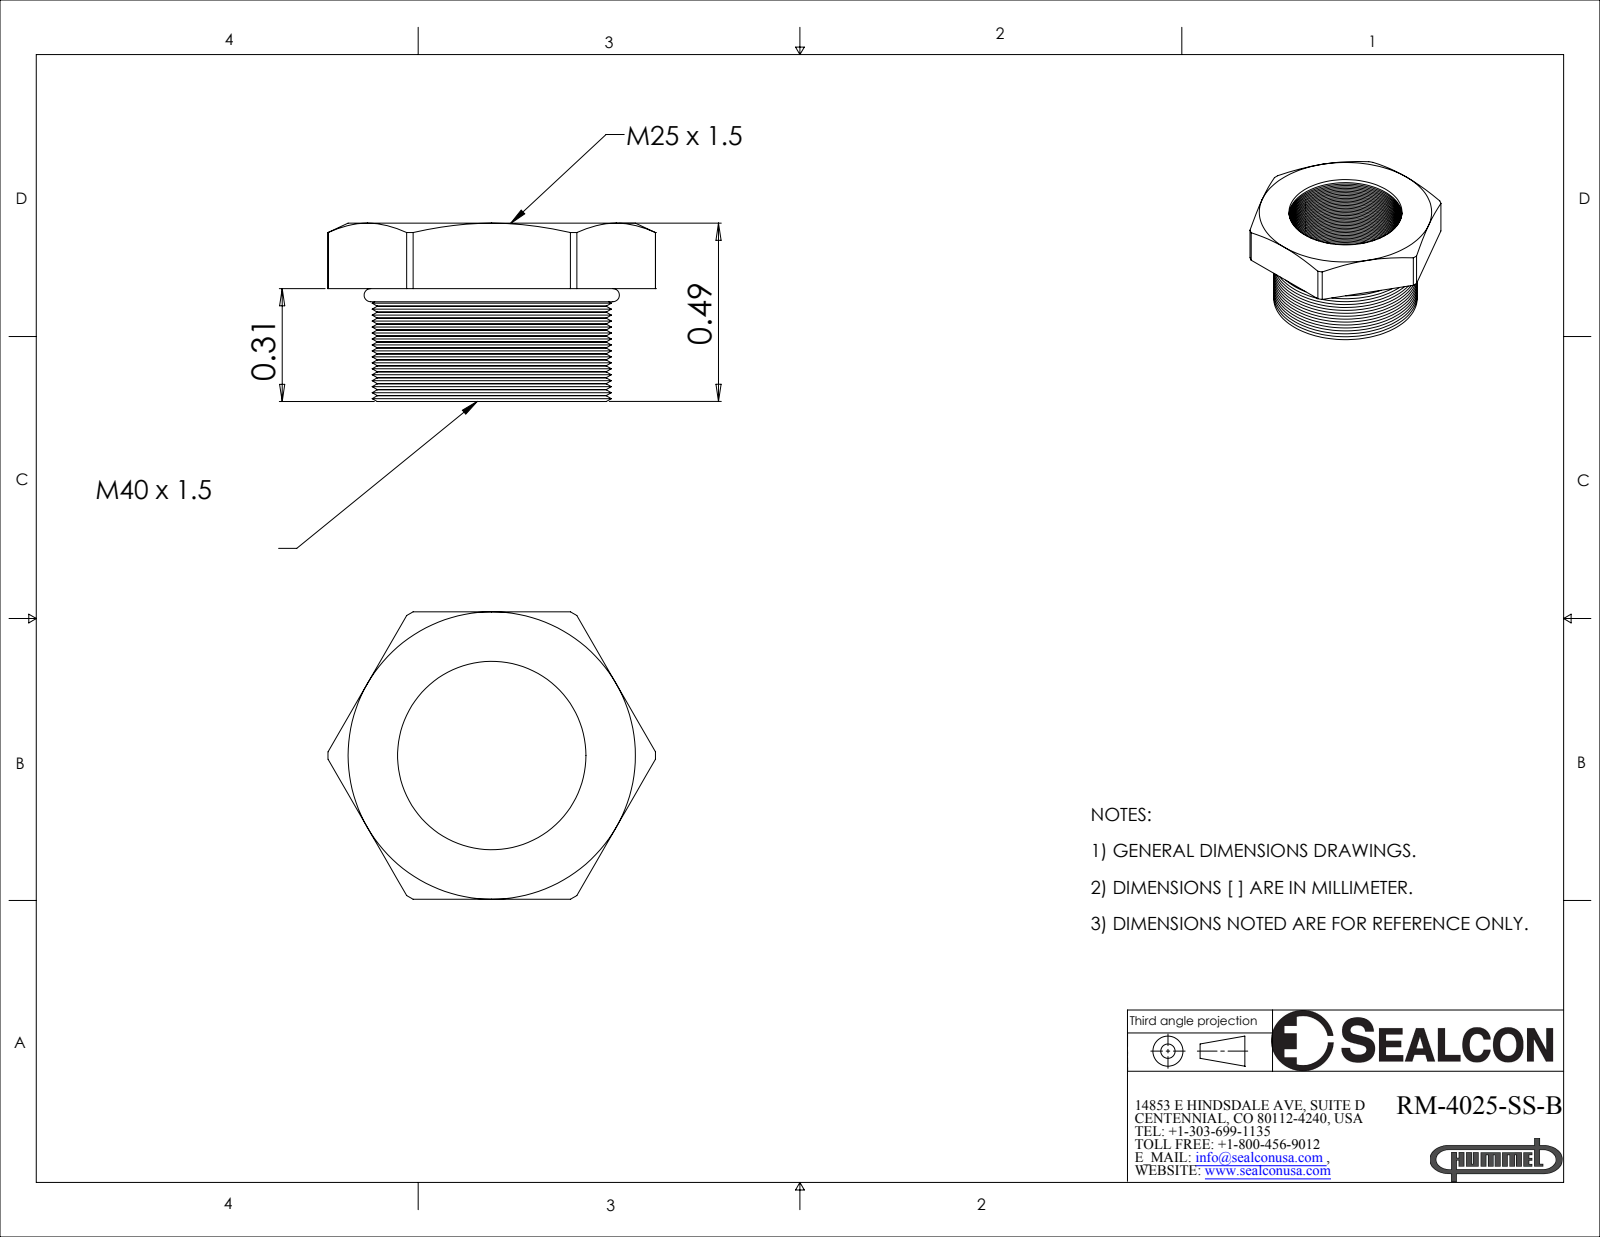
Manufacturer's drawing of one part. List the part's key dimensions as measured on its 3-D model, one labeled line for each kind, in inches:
Part name (STEP PRODUCT): RM-4025-SS-B
STEP written by: SolidWorks 2008 (CONFIG_CONTROL_DESIGN)
Units: inches
Bodies: 2 solids, 313 faces (9 planar, 105 cylindrical, 199 other)
Overall size (bounding box): 0.901 × 0.79 × 0.49
Volume: 0.094 in³ · Surface area: 4.155 in²
Round holes (diameter × count): ⌀0.518 ×1
Round bosses / shafts (diameter × count): ⌀0.63 ×1
Partial cylindrical surfaces — rounded edges, fillets, slot ends (radius × count): R0.45 ×1
Main face-to-face distances: 0.18, 0.79, 0.31, 0.49
